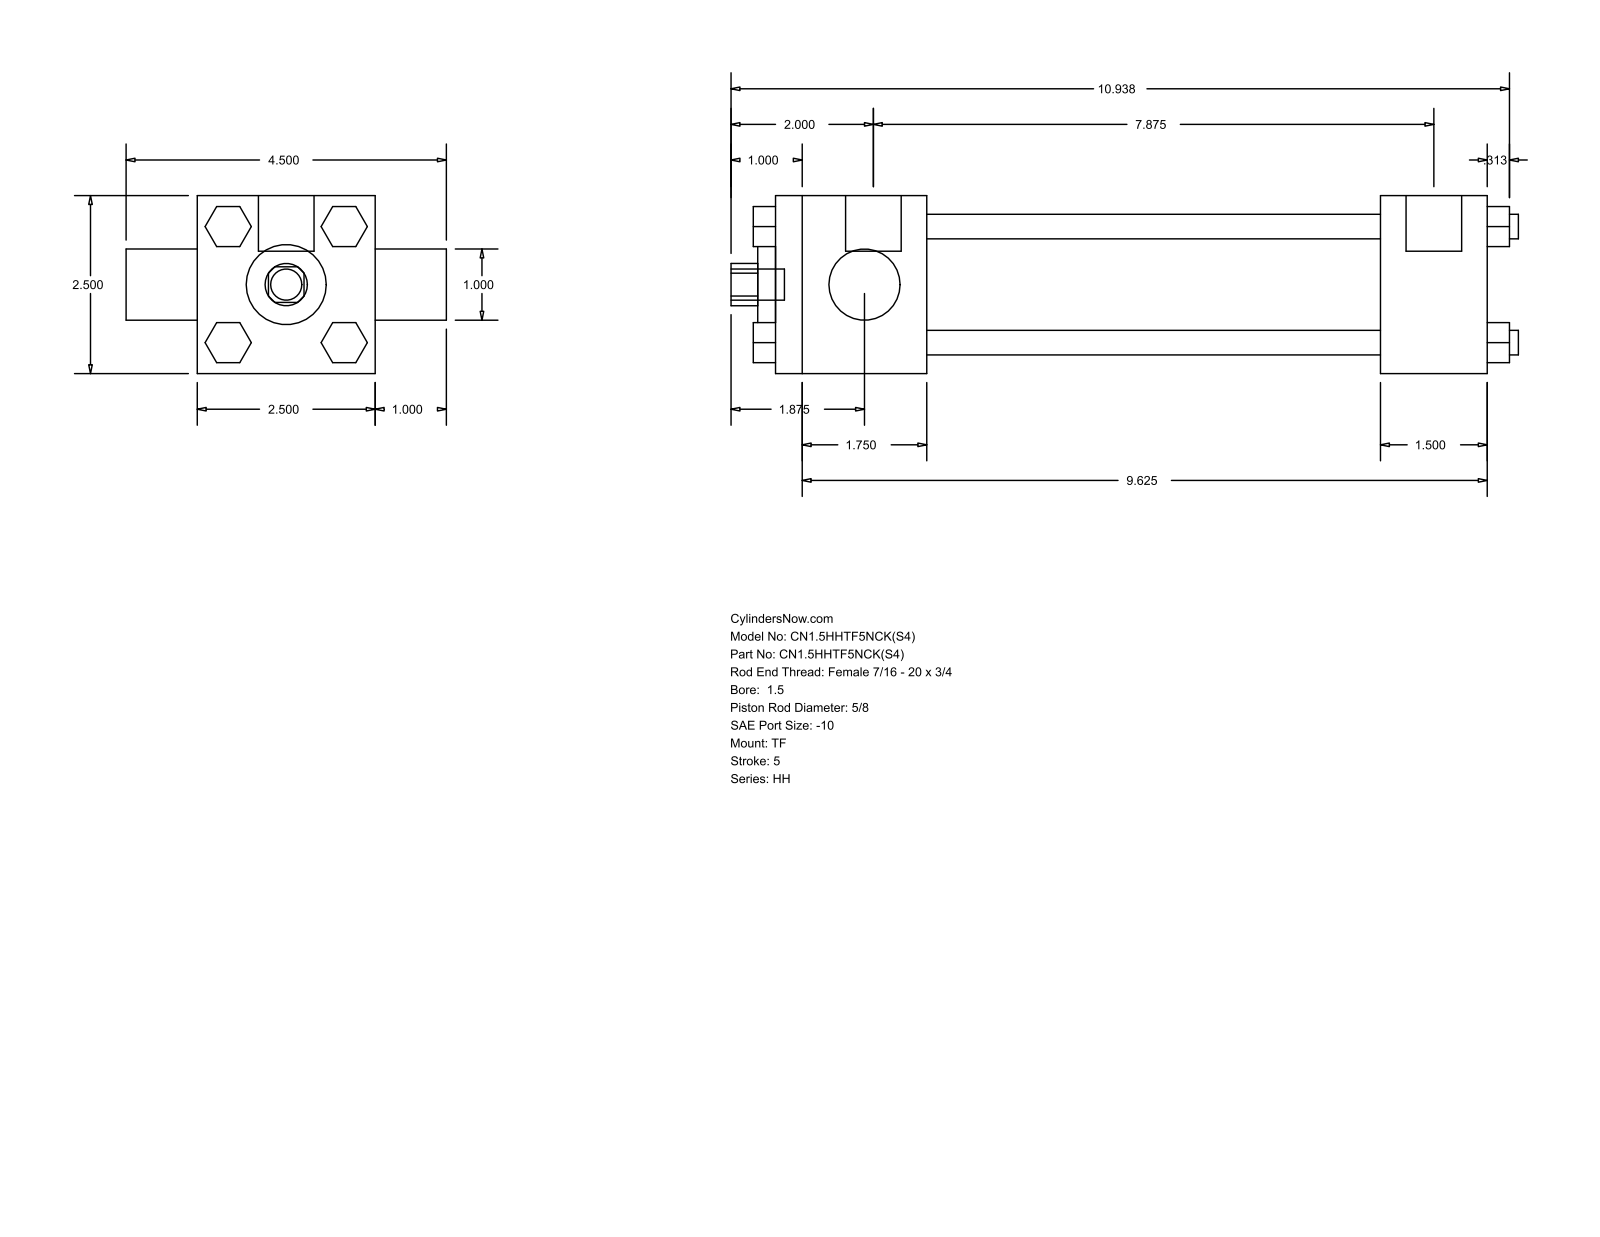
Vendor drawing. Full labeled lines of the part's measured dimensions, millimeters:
Part name (STEP PRODUCT): HH_TF__0150_0.625
STEP written by: GSSL Pune (CONFIG_CONTROL_DESIGN)
Units: millimetres
Bodies: 0 solids, 120 faces (92 planar, 28 cylindrical, 0 other)
Overall size (bounding box): 280.99 × 114.3 × 63.5
Round holes (diameter × count): ⌀15.88 ×1, ⌀25.4 ×1, ⌀28.57 ×1, ⌀44.45 ×1
Round bosses / shafts (diameter × count): ⌀8.76 ×4, ⌀5.56 ×3, ⌀19.84 ×2, ⌀11.11 ×1
Partial cylindrical surfaces — rounded edges, fillets, slot ends (radius × count): R7.54 ×1
Main face-to-face distances: 63.5, 254, 38.1, 53.97, 200.03, 215.9, 161.93, 25.4, 20.7, 14.29
